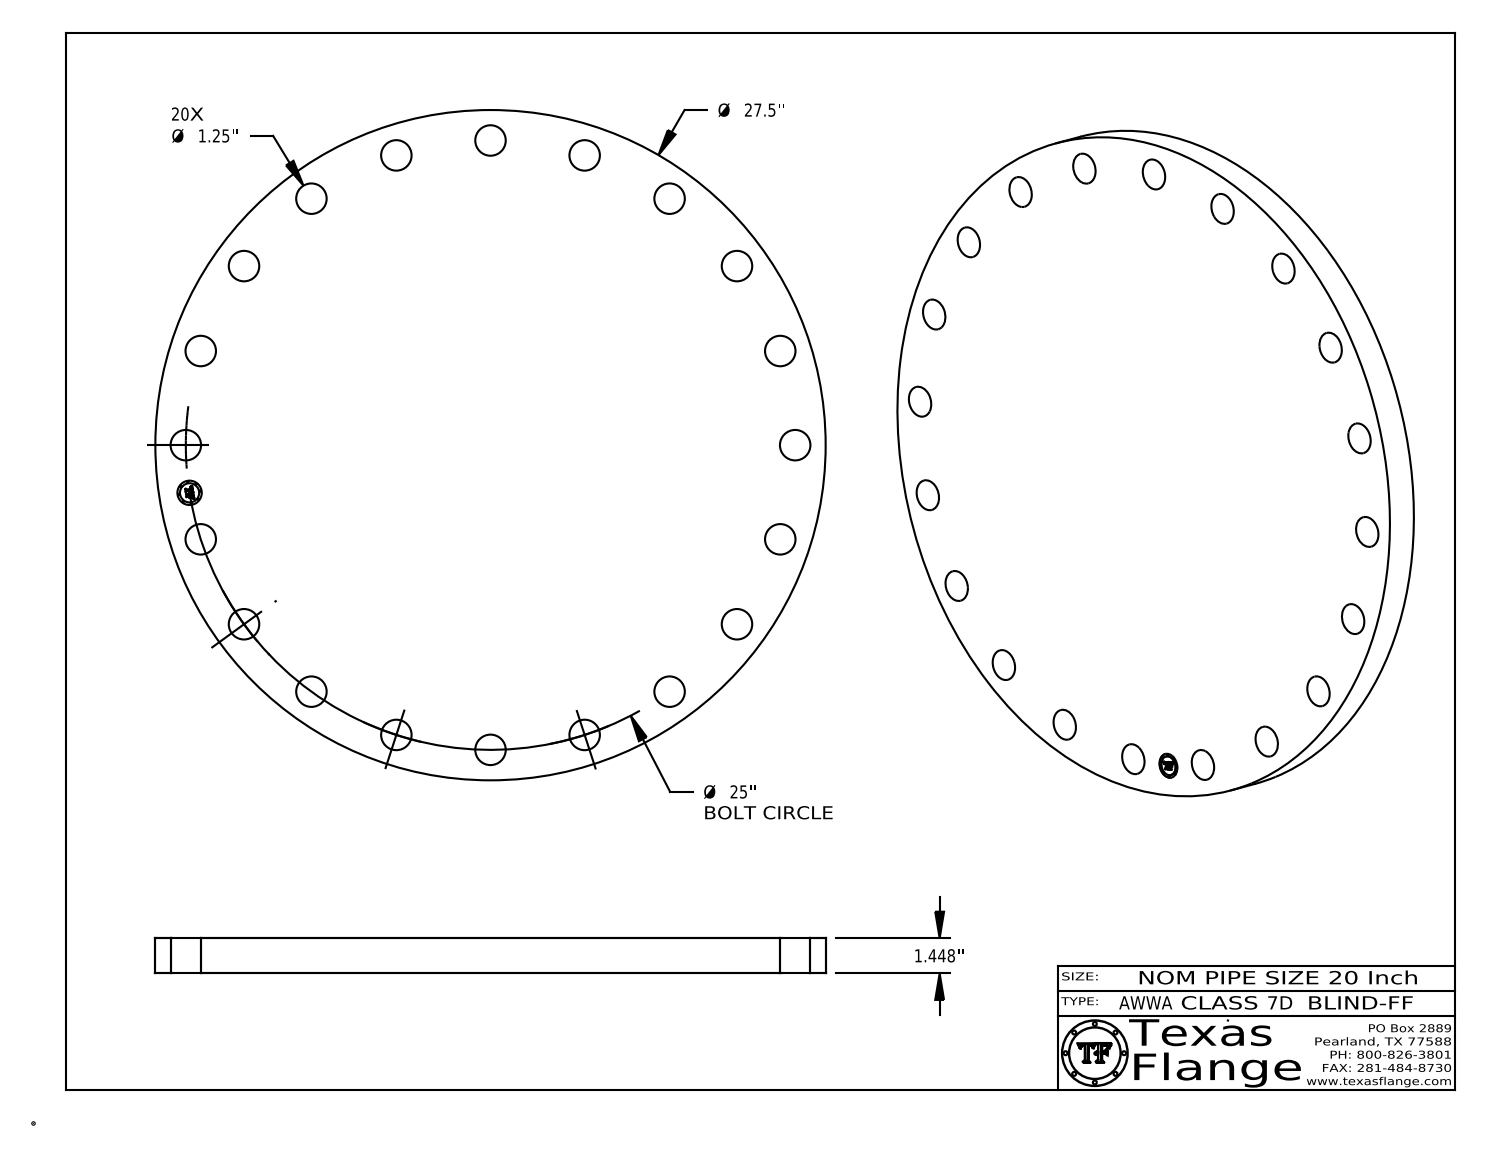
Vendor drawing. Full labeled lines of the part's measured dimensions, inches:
Part name (STEP PRODUCT): AWWA Class 7D-BLIND-FF
STEP written by: CATIA V5 STEP AP214 (AUTOMOTIVE_DESIGN)
Units: inches
Bodies: 1 solid, 429 faces (367 planar, 62 cylindrical, 0 other)
Overall size (bounding box): 27.5 × 27.5 × 1.448
Volume: 824.5 in³ · Surface area: 1 378 in²
Round holes (diameter × count): ⌀1.25 ×20, ⌀1 ×1
Round bosses / shafts (diameter × count): ⌀0.061 ×8, ⌀27.5 ×1, ⌀0.788 ×1
Main face-to-face distances: 1.448, 1.433, 0.015, 0.019, 0.298, 0.293, 0.054, 0.194, 0.248, 0.044
Hole centre spacings: 14.694, 17.678, 20.225, 23.776, 24.692, 11.35, 22.275, 3.911
